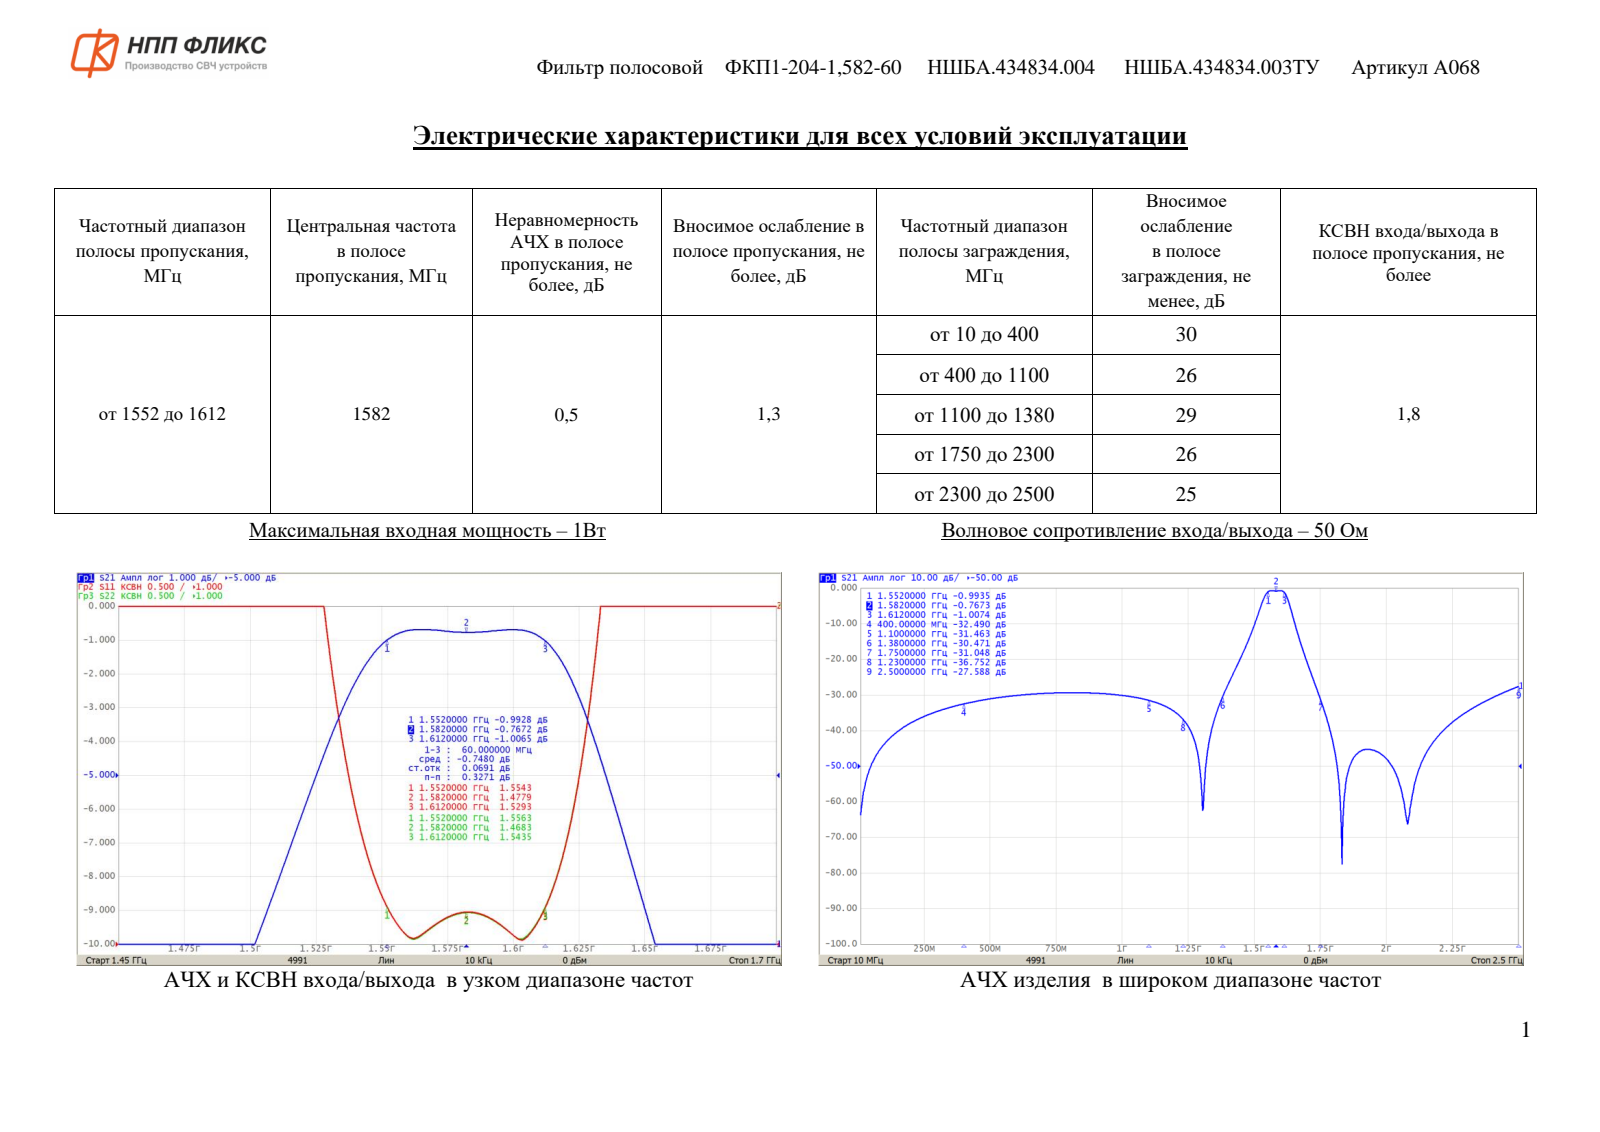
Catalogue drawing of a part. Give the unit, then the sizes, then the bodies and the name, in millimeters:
Units: millimetres
Overall size (bounding box): 7 × 6.3 × 3.6
Partial cylindrical surfaces — rounded edges, fillets, slot ends (radius × count): R0.14 ×3, R0.21 ×1, R0.24 ×1
Main face-to-face distances: 3.6, 6.3, 7, 2.6, 1.8, 3.7, 0.8, 4.5, 0.55, 1.25
Volume: 159 mm³ · Surface area: 184 mm²
Bodies: 1 solid, 343 faces (213 planar, 6 cylindrical, 124 other)
Part name (STEP PRODUCT): НШБА.434834.004_Фильтр ФКП1-204-1,582-60
STEP written by: ASCON Math Kernel (CONFIG_CONTROL_DESIGN)
